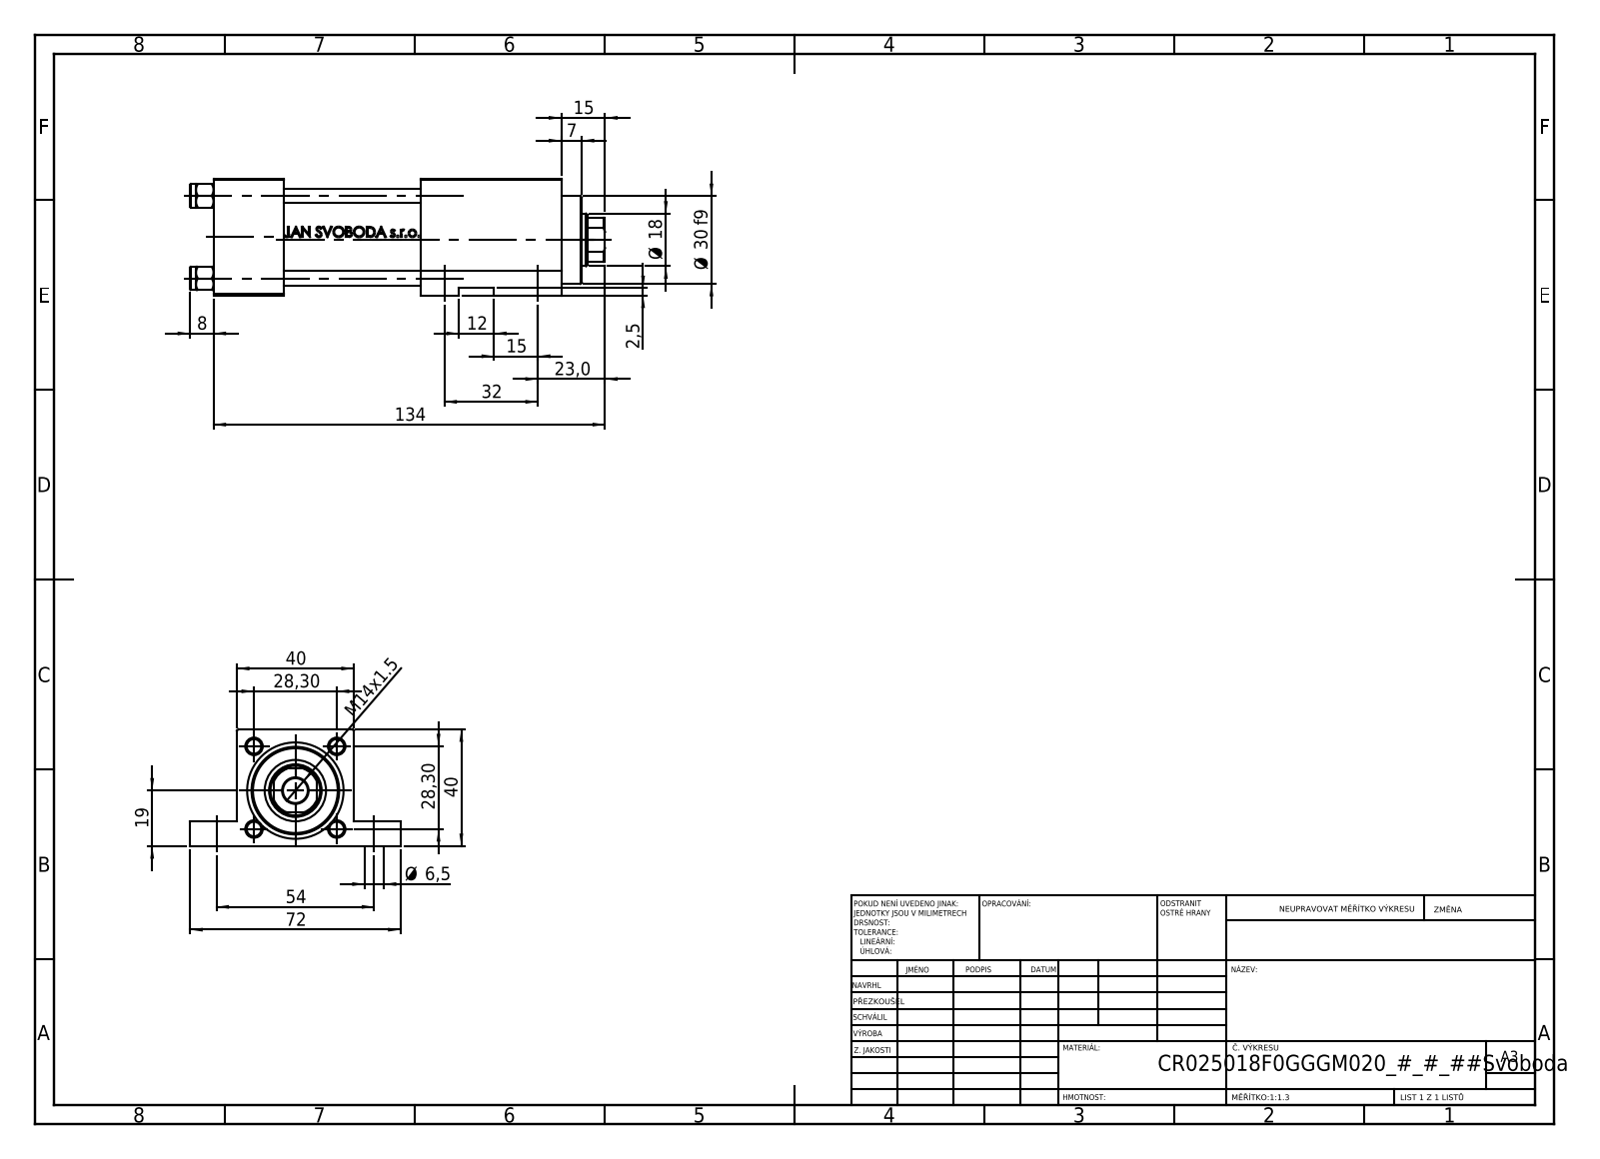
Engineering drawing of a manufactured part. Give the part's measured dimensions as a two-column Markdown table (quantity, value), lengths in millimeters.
| quantity | value |
| --- | --- |
| part name | NUT_M5_F; V215CR_F_TYCINKA; V215CR_F_Body; V215CR_VCP_F (+1 more) |
| STEP written by | SolidWorks 2019 (CONFIG_CONTROL_DESIGN) |
| units | millimeters |
| bodies | 11 solids, 1100 faces (436 planar, 124 cylindrical, 540 other) |
| overall size | 142 × 72 × 40 |
| volume | 159 643 mm³ |
| surface area | 60 924 mm² |
| round holes (diameter × count) | 5 × 4, 6.5 × 4, 20 × 3, 7 × 2, 13.16 × 2, 8.5 × 1, 18 × 1, 21 × 1, 25 × 1, 30 × 1 |
| round bosses / shafts (diameter × count) | 8 × 4, 31 × 1 |
| partial cylindrical surfaces (radius × count) | 8.5 × 1 |
| main face-to-face distances | 40, 24, 8.5, 31.5, 71, 47, 48, 6, 119, 95 |
| hole center spacings | 28.3, 19.32, 20.73, 27.46, 32, 38.18, 40.02, 54 |
